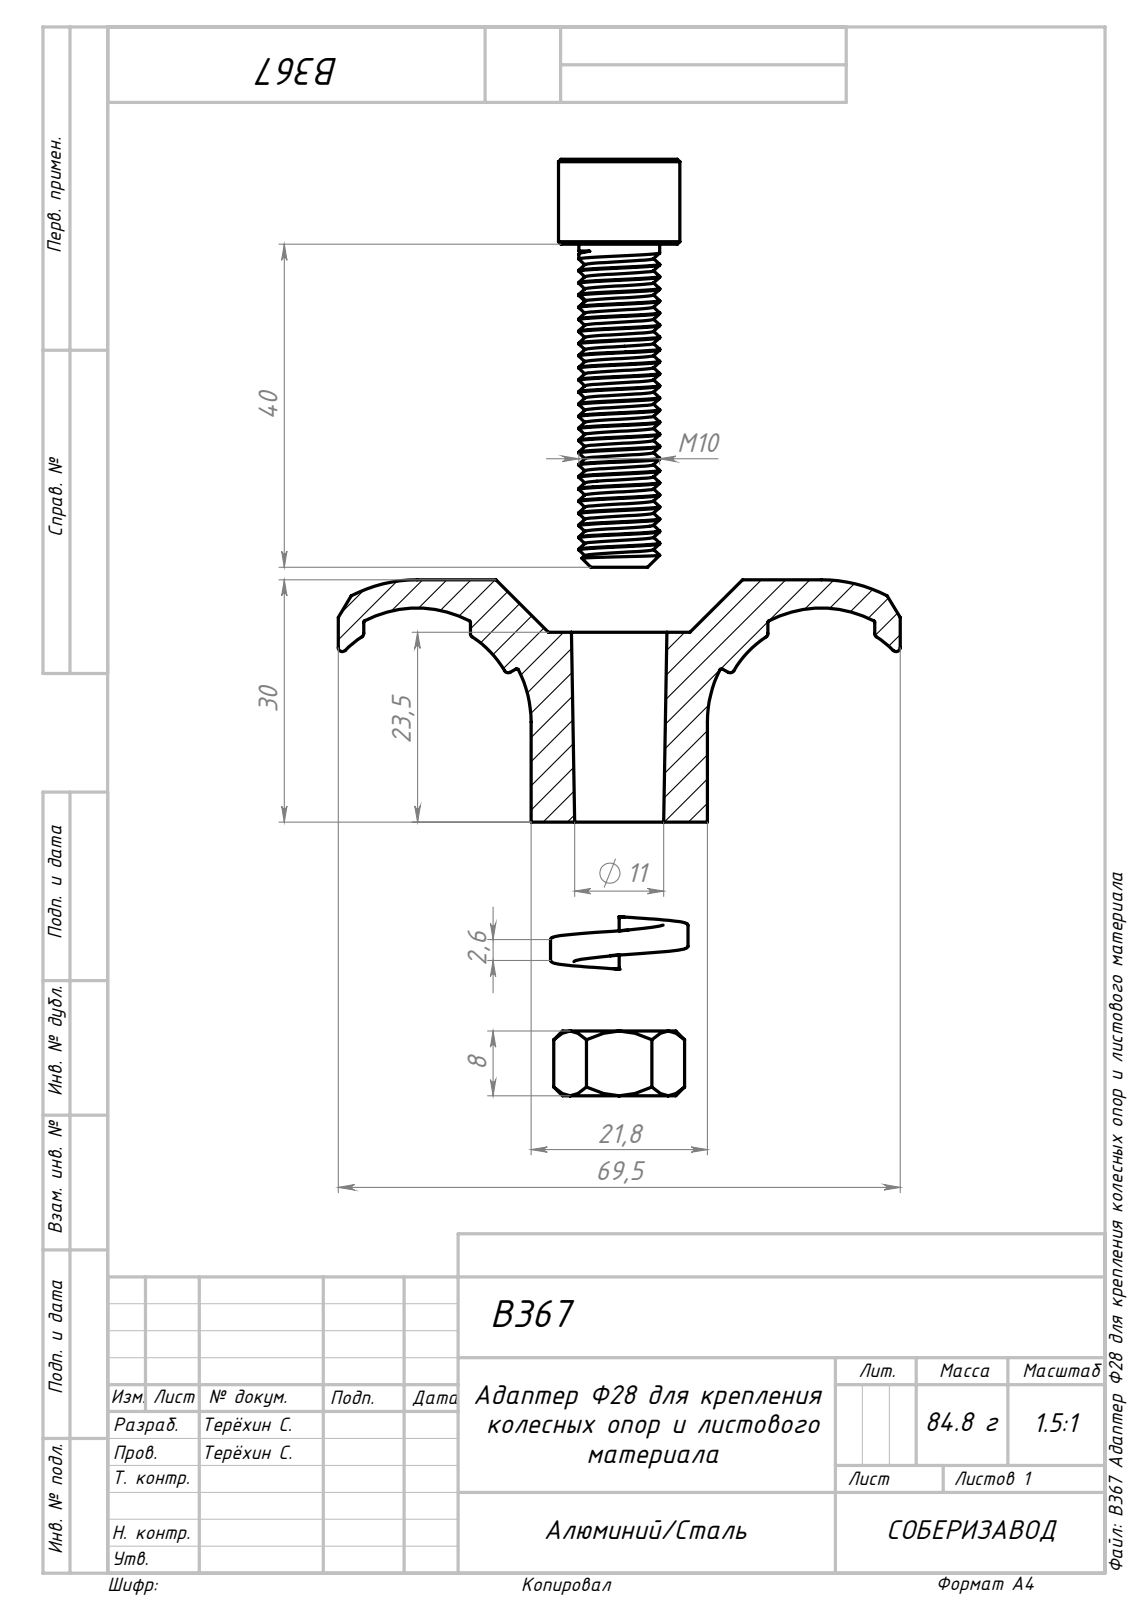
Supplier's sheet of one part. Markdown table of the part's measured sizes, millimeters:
| quantity | value |
| --- | --- |
| part name | B367 Адаптер Ф28 для крепления колесных опор и листового материала |
| STEP written by | SolidWorks 2022 (AUTOMOTIVE_DESIGN) |
| units | millimeters |
| bodies | 4 solids, 202 faces (48 planar, 89 cylindrical, 65 other) |
| overall size | 115.89 × 69.5 × 30 |
| volume | 22 760 mm³ |
| surface area | 14 302 mm² |
| round holes (diameter × count) | 8.5 × 1 |
| round bosses / shafts (diameter × count) | 15 × 1, 10 × 1 |
| partial cylindrical surfaces (radius × count) | 0.5 × 12, 0.2 × 6, 12.55 × 2, 14.1 × 2, 17.6 × 2 |
| main face-to-face distances | 30, 6.5, 21.8, 23.5, 23.85, 45.65, 2.9, 11.1, 19, 4.5 |
